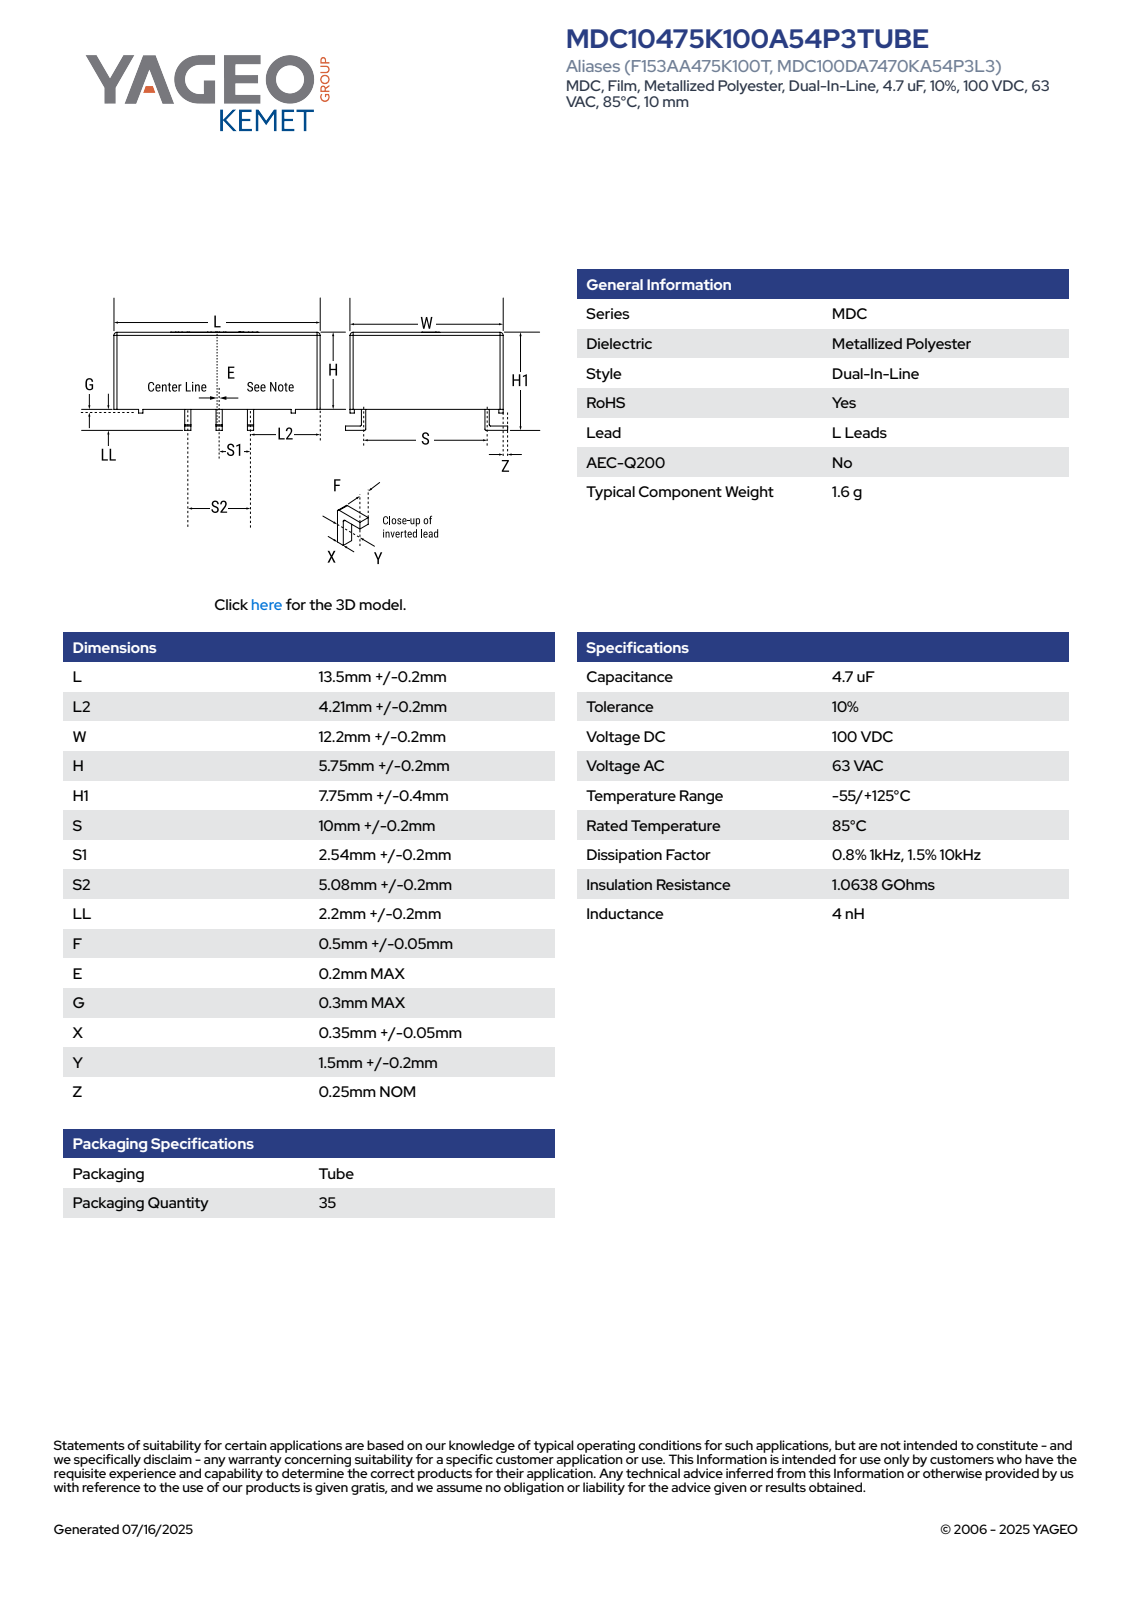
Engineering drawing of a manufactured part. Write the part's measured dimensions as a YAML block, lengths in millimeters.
part_name: "CFS_KD6MDC_A54_L13.7L24.41W12.4H5.95S10LL2.4"
step_written_by: "SolidWorks 2021 (AUTOMOTIVE_DESIGN)"
units: millimeters
bodies: {solids: 4, faces: 117, planar: 113, cylindrical: 0, other: 4}
overall_size: [13.7, 13.2, 8.36]
volume: 1010
surface_area: 689
face_to_face_distances: [5.95, 12.4, 13.7, 0.4, 1.3, 11.5, 11.1, 0.9, 10.2, 4.03]
